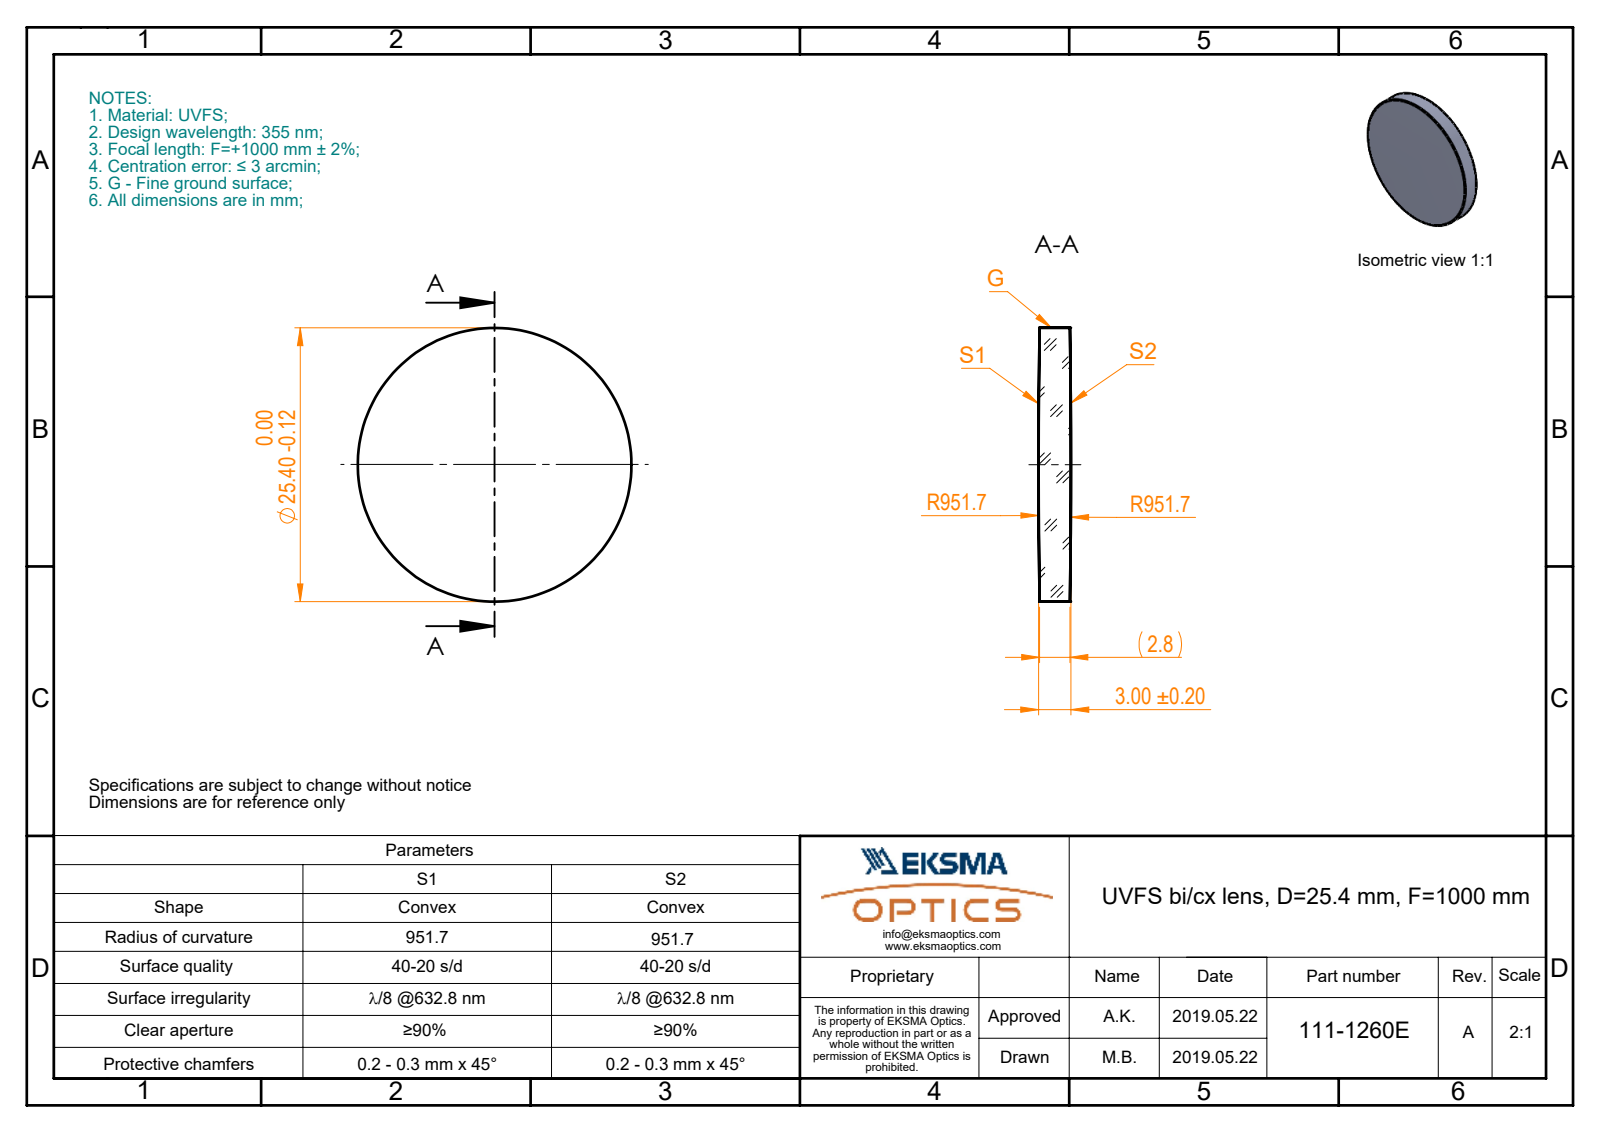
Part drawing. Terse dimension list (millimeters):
name: 111-1260E UVFS bi-cx 25.4 F1000
written by: SolidWorks 2017 (CONFIG_CONTROL_DESIGN)
unit: mm
bodies: 1 solid, 6 faces (0 planar, 2 cylindrical, 4 other)
size: 25.4 × 25.4 × 3
volume: 1 477 mm³; area: 1 239 mm²
bosses: 1× ⌀25.4
